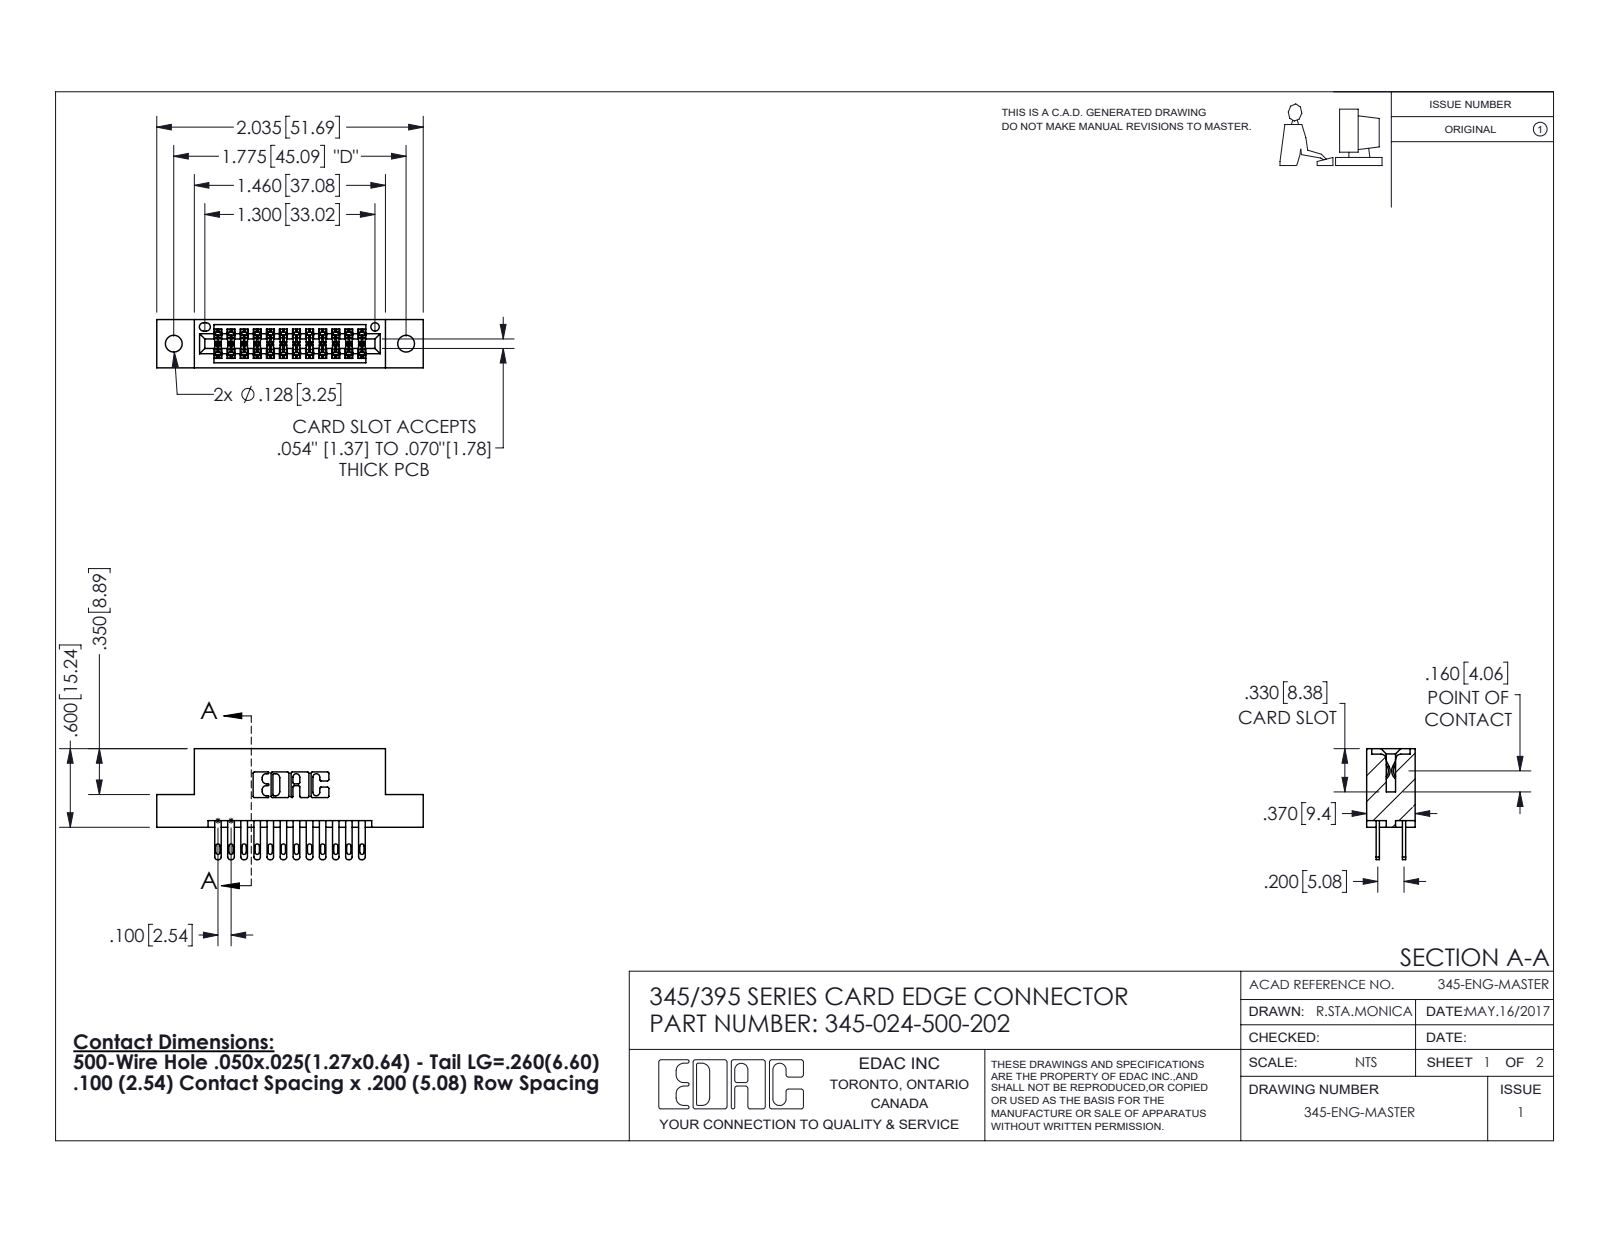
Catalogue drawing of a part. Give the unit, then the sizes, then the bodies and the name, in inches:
Units: inches
Overall size (bounding box): 2.035 × 0.847 × 0.37
Round holes (diameter × count): ⌀0.128 ×2, ⌀0.064 ×1
Partial cylindrical surfaces — rounded edges, fillets, slot ends (radius × count): R0.006 ×36, R0.016 ×24, R0.02 ×24, R0.01 ×22, R0.007 ×6, R0.031 ×6, R0.026 ×3, R0.014 ×2
Main face-to-face distances: 0.2, 0.298, 0.072, 0.098, 0.272, 0.025, 0.37, 0.225, 0.1, 0.175
Hole centre spacings: 0.27, 1.543, 1.775
Volume: 0.292 in³ · Surface area: 10.01 in²
Bodies: 25 solids, 1230 faces (728 planar, 502 cylindrical, 0 other)
Part name (STEP PRODUCT): 345 Part_Flush Mounting Lugs - 0.128 Dia; 345-292-001_345-293-100; 345-024-500-202
STEP written by: SolidWorks 2016 (CONFIG_CONTROL_DESIGN)
